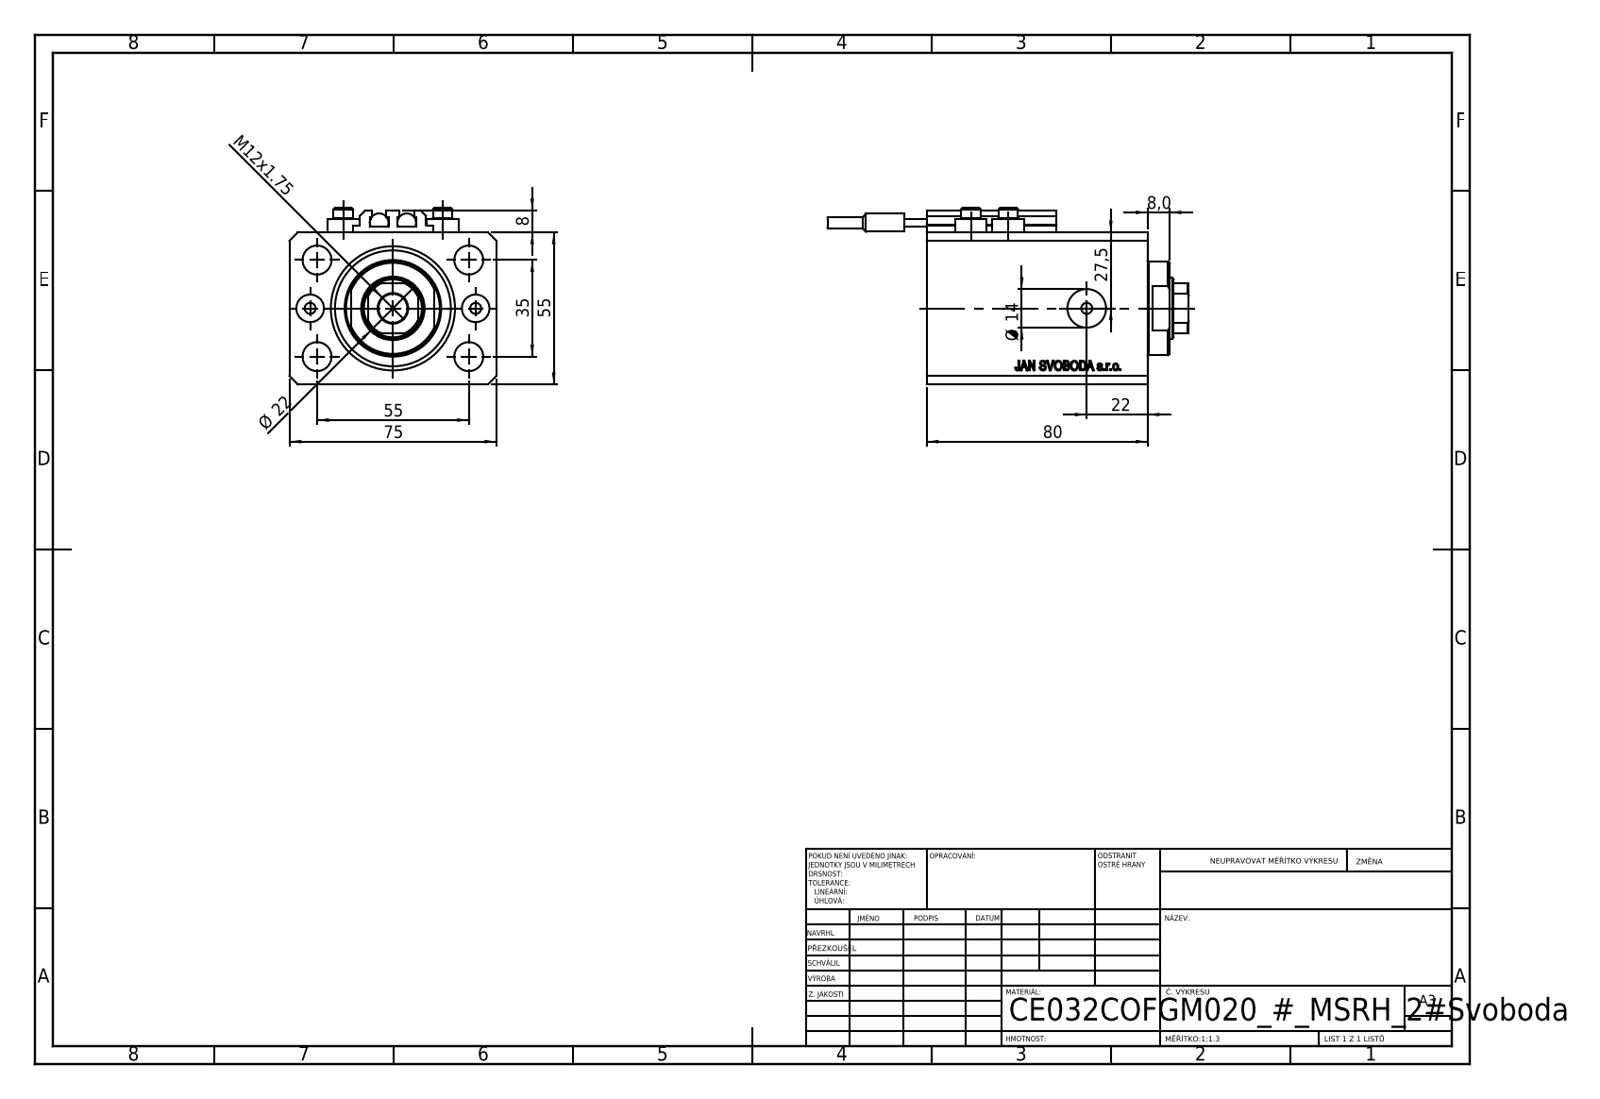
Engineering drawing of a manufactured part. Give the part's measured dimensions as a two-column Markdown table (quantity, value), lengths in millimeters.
| quantity | value |
| --- | --- |
| part name | V250CE_VC_C; V250CE_C_VCP; ALLEN BOLT V250CE; V250CE_C_Body (+1 more) |
| STEP written by | SolidWorks 2019 (CONFIG_CONTROL_DESIGN) |
| units | millimeters |
| bodies | 10 solids, 1086 faces (536 planar, 98 cylindrical, 452 other) |
| overall size | 131 × 75 × 64 |
| volume | 308 623 mm³ |
| surface area | 74 206 mm² |
| round holes (diameter × count) | 4 × 8, 10.5 × 5, 10 × 2, 14 × 2, 22 × 1, 32 × 1, 45 × 1 |
| round bosses / shafts (diameter × count) | 11.6 × 4, 7 × 4, 6.8 × 2, 6.5 × 2, 4 × 2, 34 × 1 |
| partial cylindrical surfaces (radius × count) | 0.2 × 10, 10.5 × 1 |
| main face-to-face distances | 55, 75, 80, 15, 65, 9.9, 55.1, 70.1, 3, 2 |
| hole center spacings | 17.68, 32.6, 60.1, 36, 13.6, 30, 35, 38.48 |
